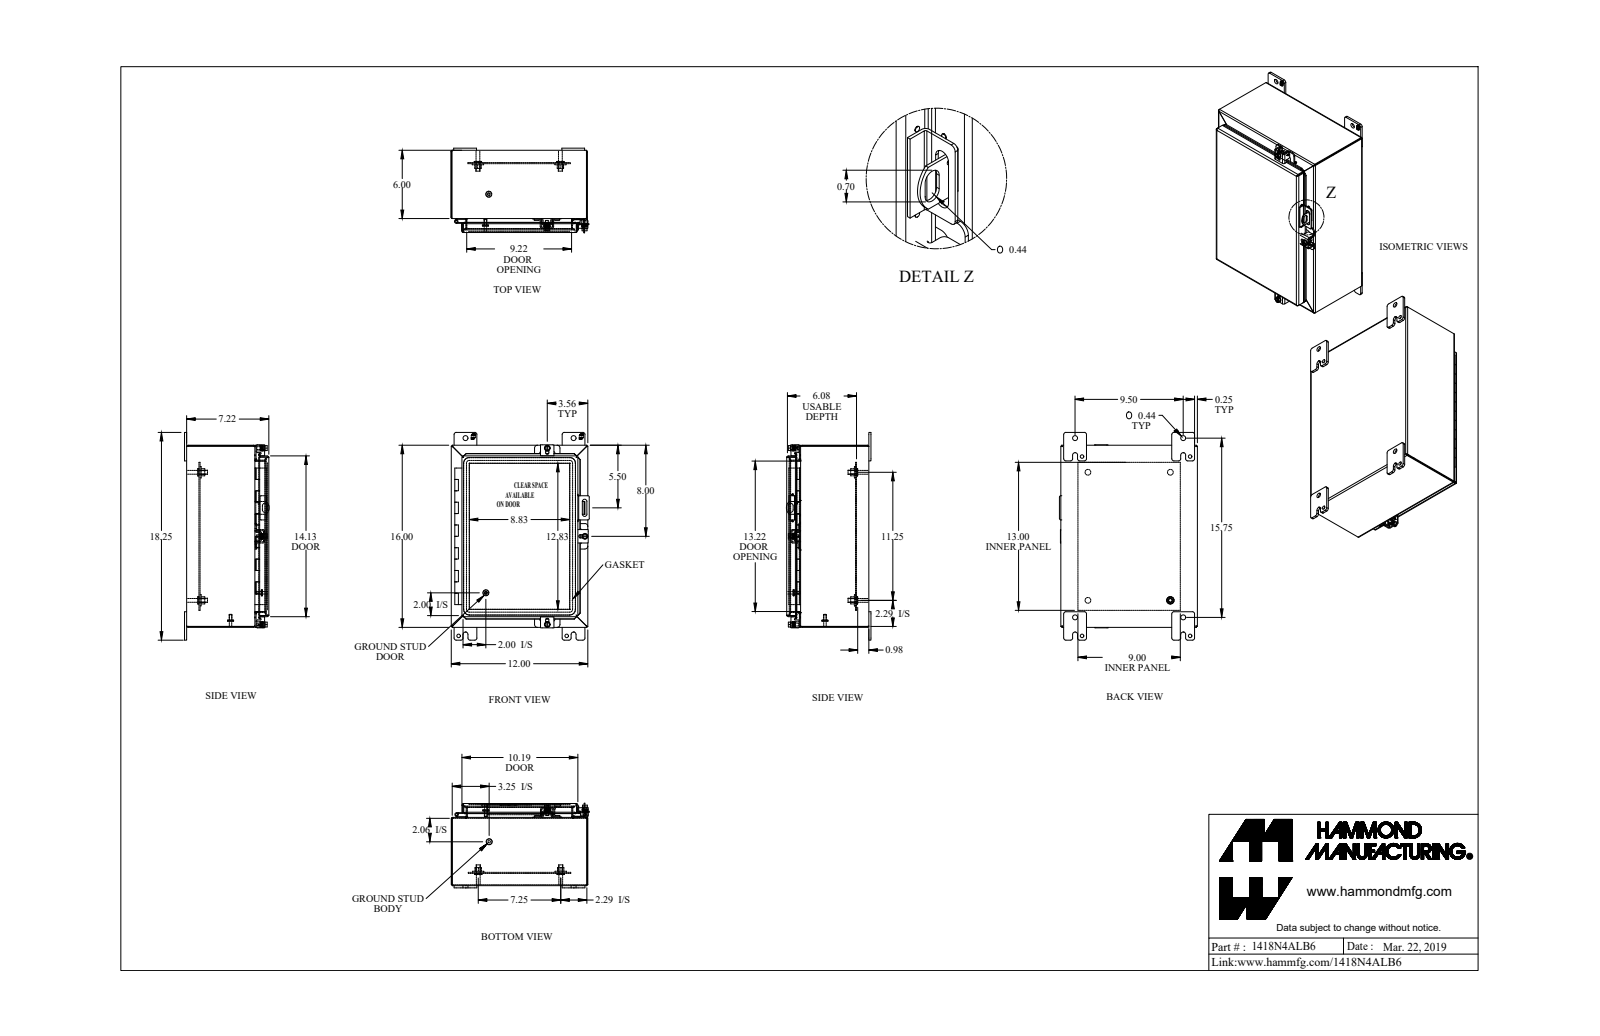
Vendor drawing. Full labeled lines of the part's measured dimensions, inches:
Part name (STEP PRODUCT): 1418N4ALB6
STEP written by: SolidWorks 2019 (AUTOMOTIVE_DESIGN)
Units: inches
Bodies: 34 solids, 1174 faces (765 planar, 317 cylindrical, 92 other)
Overall size (bounding box): 18.25 × 12.126 × 7.438
Volume: 93.01 in³ · Surface area: 2 159 in²
Round holes (diameter × count): ⌀0.313 ×4, ⌀0.437 ×4, ⌀0.5 ×4, ⌀0.232 ×3, ⌀0.265 ×3, ⌀0.375 ×3, ⌀0.307 ×2, ⌀0.445 ×2, ⌀0.125 ×1, ⌀0.187 ×1
Round bosses / shafts (diameter × count): ⌀0.131 ×10, ⌀0.65 ×4, ⌀0.375 ×4, ⌀0.33 ×4, ⌀0.5 ×3, ⌀0.4 ×3, ⌀0.244 ×3, ⌀1 ×2
Partial cylindrical surfaces — rounded edges, fillets, slot ends (radius × count): R0.188 ×24, R0.05 ×18, R0.15 ×18, R0.041 ×16, R0.122 ×16, R0.25 ×16, R0.125 ×9, R0.218 ×8
Main face-to-face distances: 0.081, 11.919, 0.1, 7.041, 7.122, 15.919, 7.141, 7.222, 5.919, 0.095
Hole centre spacings: 1.736, 9.5, 15.75, 18.393, 3.204, 7.25, 11.25, 12.8
